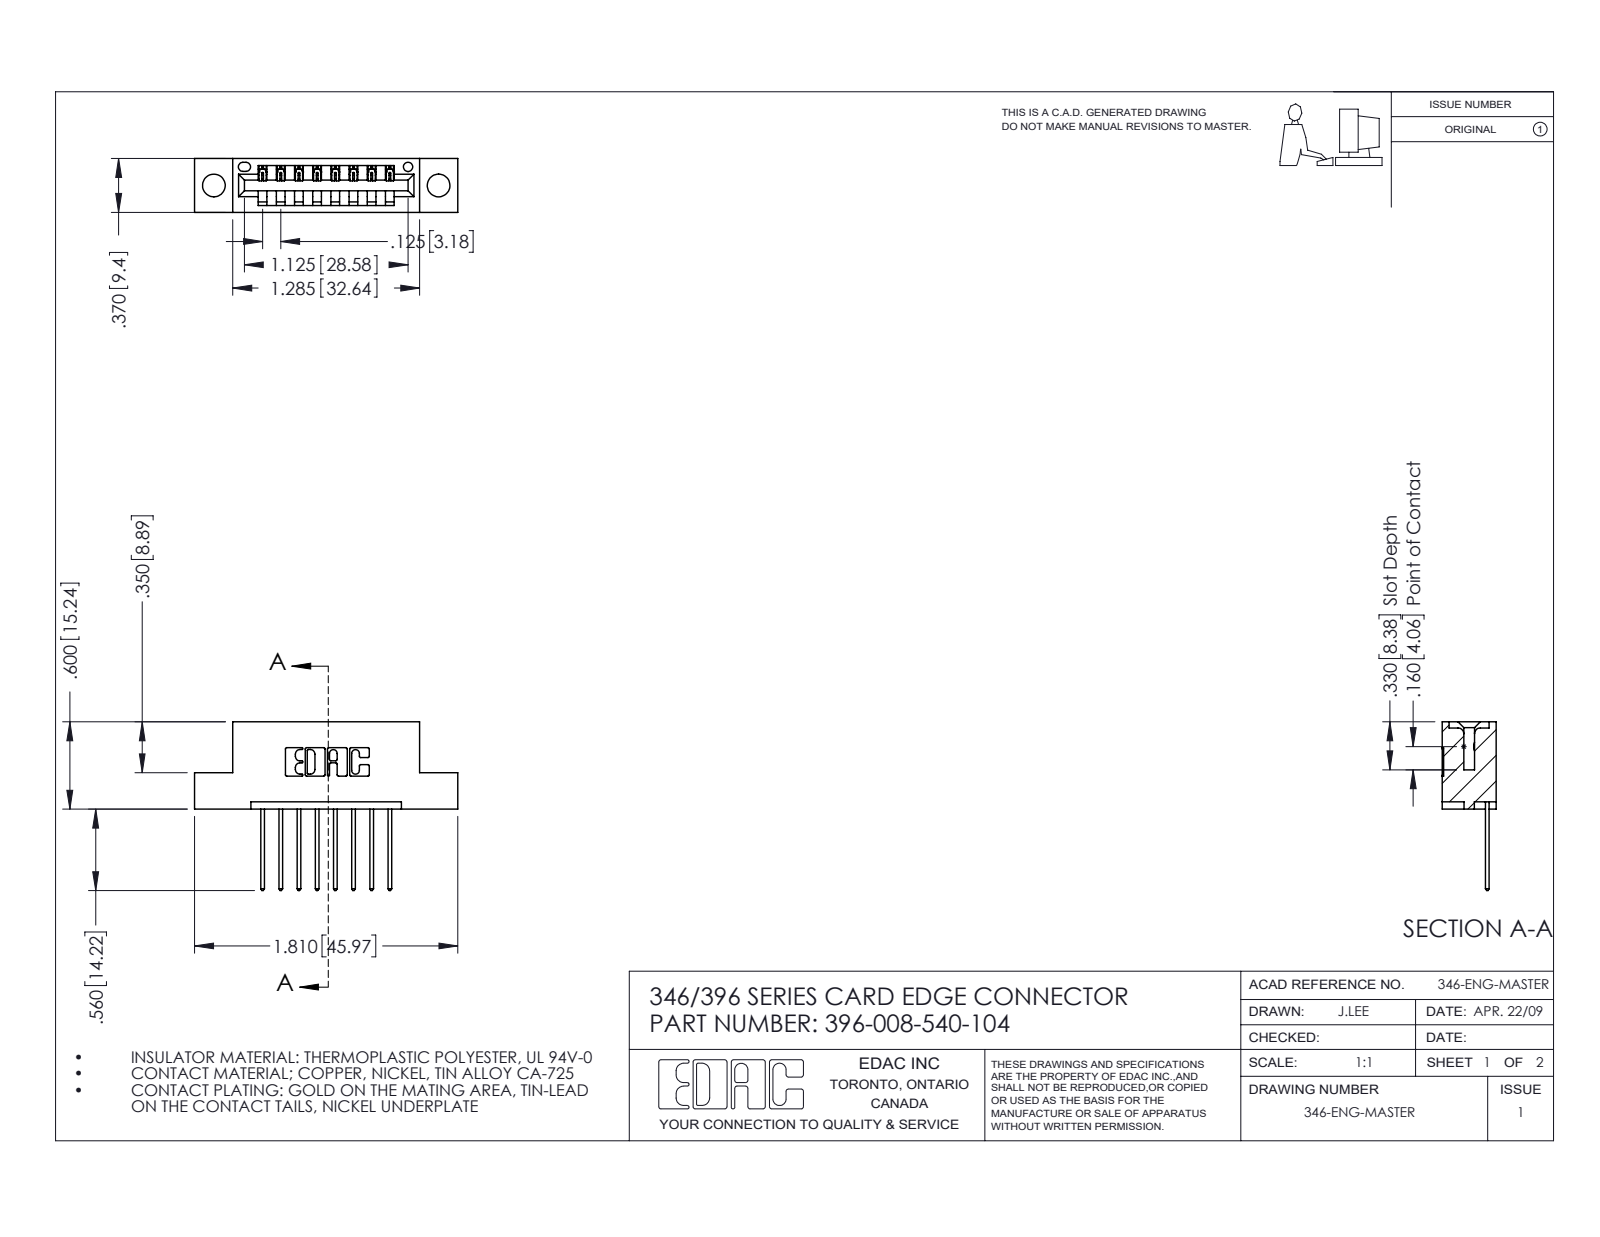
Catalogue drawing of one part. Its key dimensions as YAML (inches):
part_name: "396-008-540-104; 346 Part_Flush Mounting Lugs - 0.156 Dia-TH; 345-292-001_345-293-140"
step_written_by: "SolidWorks 2016 (CONFIG_CONTROL_DESIGN)"
units: inches
bodies: {solids: 9, faces: 586, planar: 396, cylindrical: 190, other: 0}
overall_size: [1.81, 1.16, 0.37]
volume: 0.25
surface_area: 7.174
round_holes:
  - {diameter: 0.156, count: 2}
  - {diameter: 0.064, count: 1}
partial_cylinders:
  - {radius: 0.01, count: 22}
  - {radius: 0.006, count: 16}
  - {radius: 0.01, count: 16}
  - {radius: 0.007, count: 6}
  - {radius: 0.031, count: 6}
  - {radius: 0.026, count: 3}
  - {radius: 0.031, count: 2}
  - {radius: 0.04, count: 2}
face_to_face_distances: [0.25, 0.048, 0.322, 0.37, 0.072, 0.298, 0.025, 0.5, 0.148, 0.222]
hole_center_spacings: [0.246, 1.341, 1.545]
